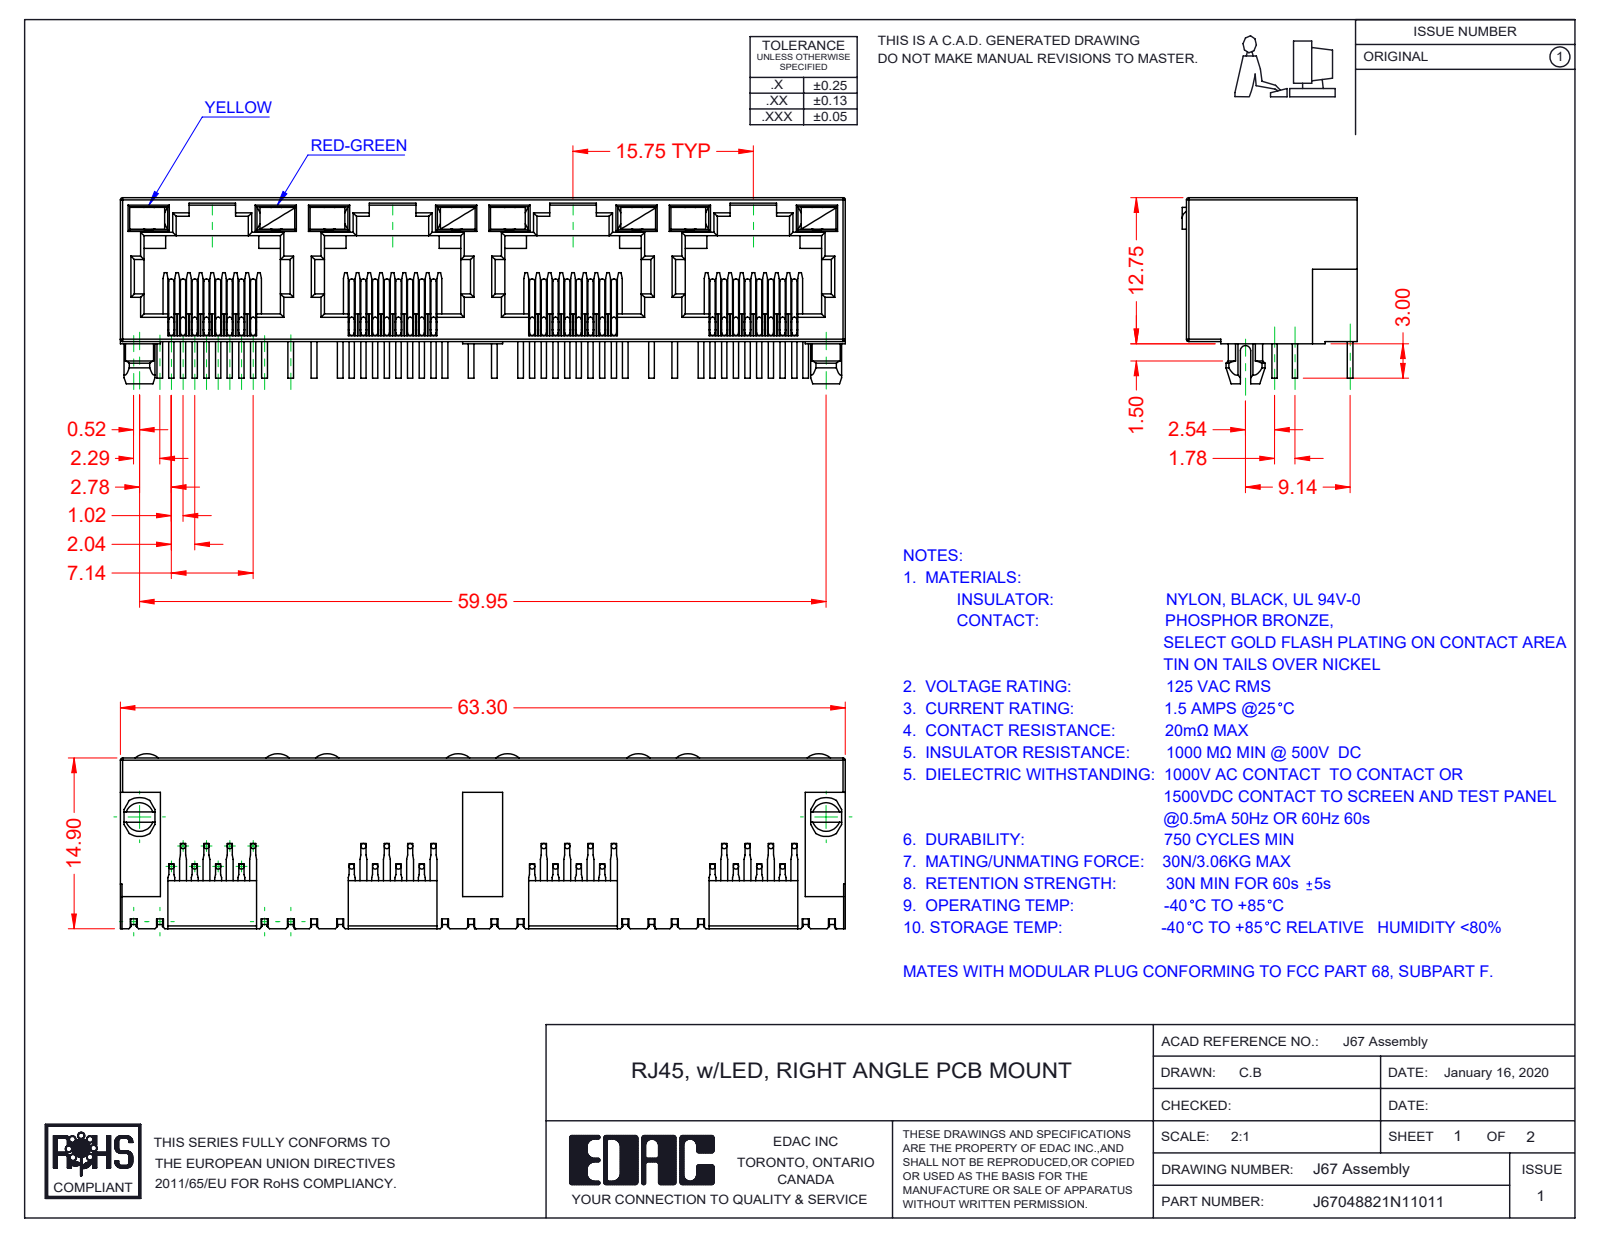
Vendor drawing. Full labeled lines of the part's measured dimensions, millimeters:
Part name (STEP PRODUCT): J67048822N16011; 67 LED LH_1-Yellow; 67 LED RH_6-Red-Green; 67 Contacts (+1 more)
STEP written by: SolidWorks 2016 (CONFIG_CONTROL_DESIGN)
Units: millimetres
Bodies: 41 solids, 2473 faces (1781 planar, 484 cylindrical, 208 other)
Overall size (bounding box): 63.3 × 16.25 × 15.28
Volume: 5 159 mm³ · Surface area: 11 573 mm²
Round bosses / shafts (diameter × count): ⌀0.46 ×96
Partial cylindrical surfaces — rounded edges, fillets, slot ends (radius × count): R0.2 ×66, R0.3 ×29, R0.45 ×9, R1.55 ×8, R1.5 ×2, R1.7 ×2, R0.35 ×1, R1 ×1
Main face-to-face distances: 0.5, 12.55, 1.89, 0.89, 10, 15.75, 1, 1.39, 11, 11.89
